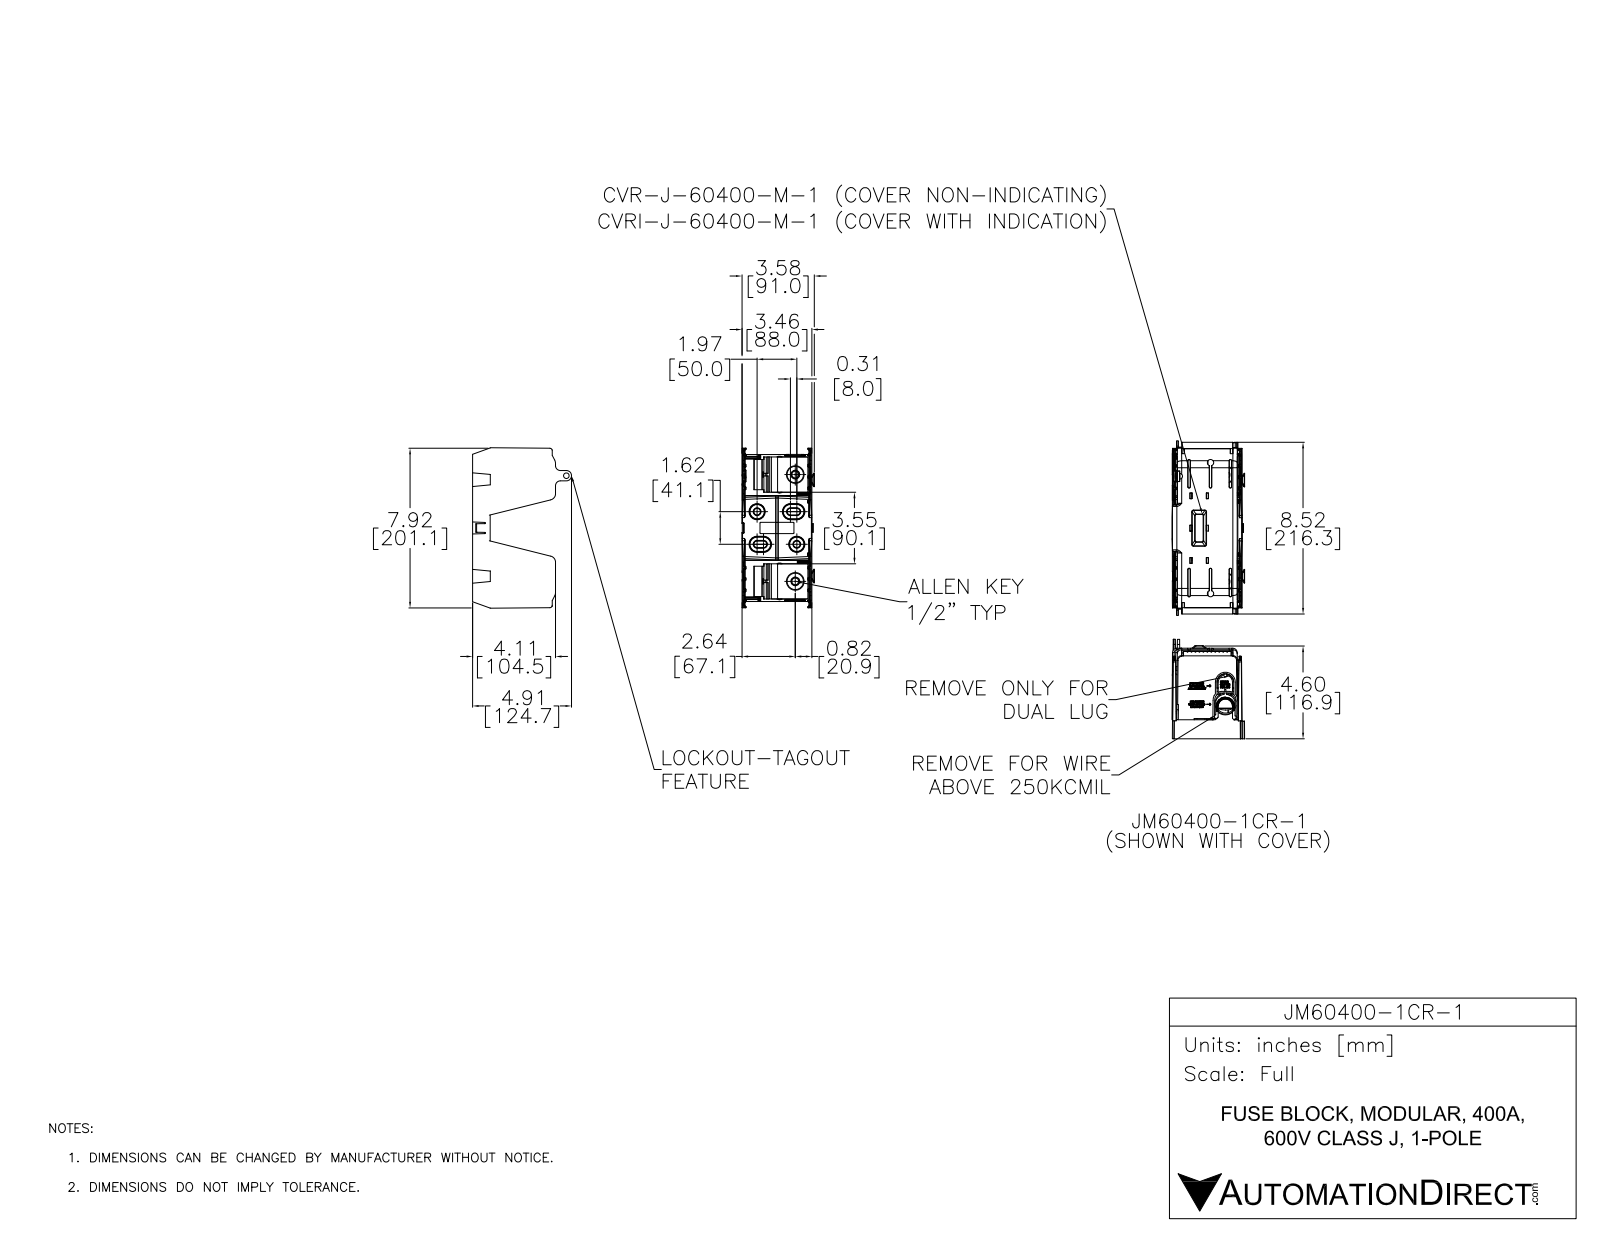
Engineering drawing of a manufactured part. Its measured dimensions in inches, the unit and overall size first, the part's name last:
Units: inches
Overall size (bounding box): 7.957 × 4.768 × 3.602
Round holes (diameter × count): ⌀0.937 ×1
Round bosses / shafts (diameter × count): ⌀0.196 ×4, ⌀0.875 ×2, ⌀0.28 ×2, ⌀0.277 ×1
Partial cylindrical surfaces — rounded edges, fillets, slot ends (radius × count): R0.02 ×138, R0.01 ×42, R0.014 ×24, R0.015 ×24, R0.01 ×16, R0.119 ×10, R0.01 ×9, R0.039 ×4
Main face-to-face distances: 3.336, 3.336, 0.95, 0.048, 0.125, 0.125, 0.998, 0.173, 1.122, 5.323
Bodies: 0 solids, 972 faces (287 planar, 418 cylindrical, 267 other)
Part name (STEP PRODUCT): JM60400-1CR-1
STEP written by: SolidWorks 2021 (CONFIG_CONTROL_DESIGN)
